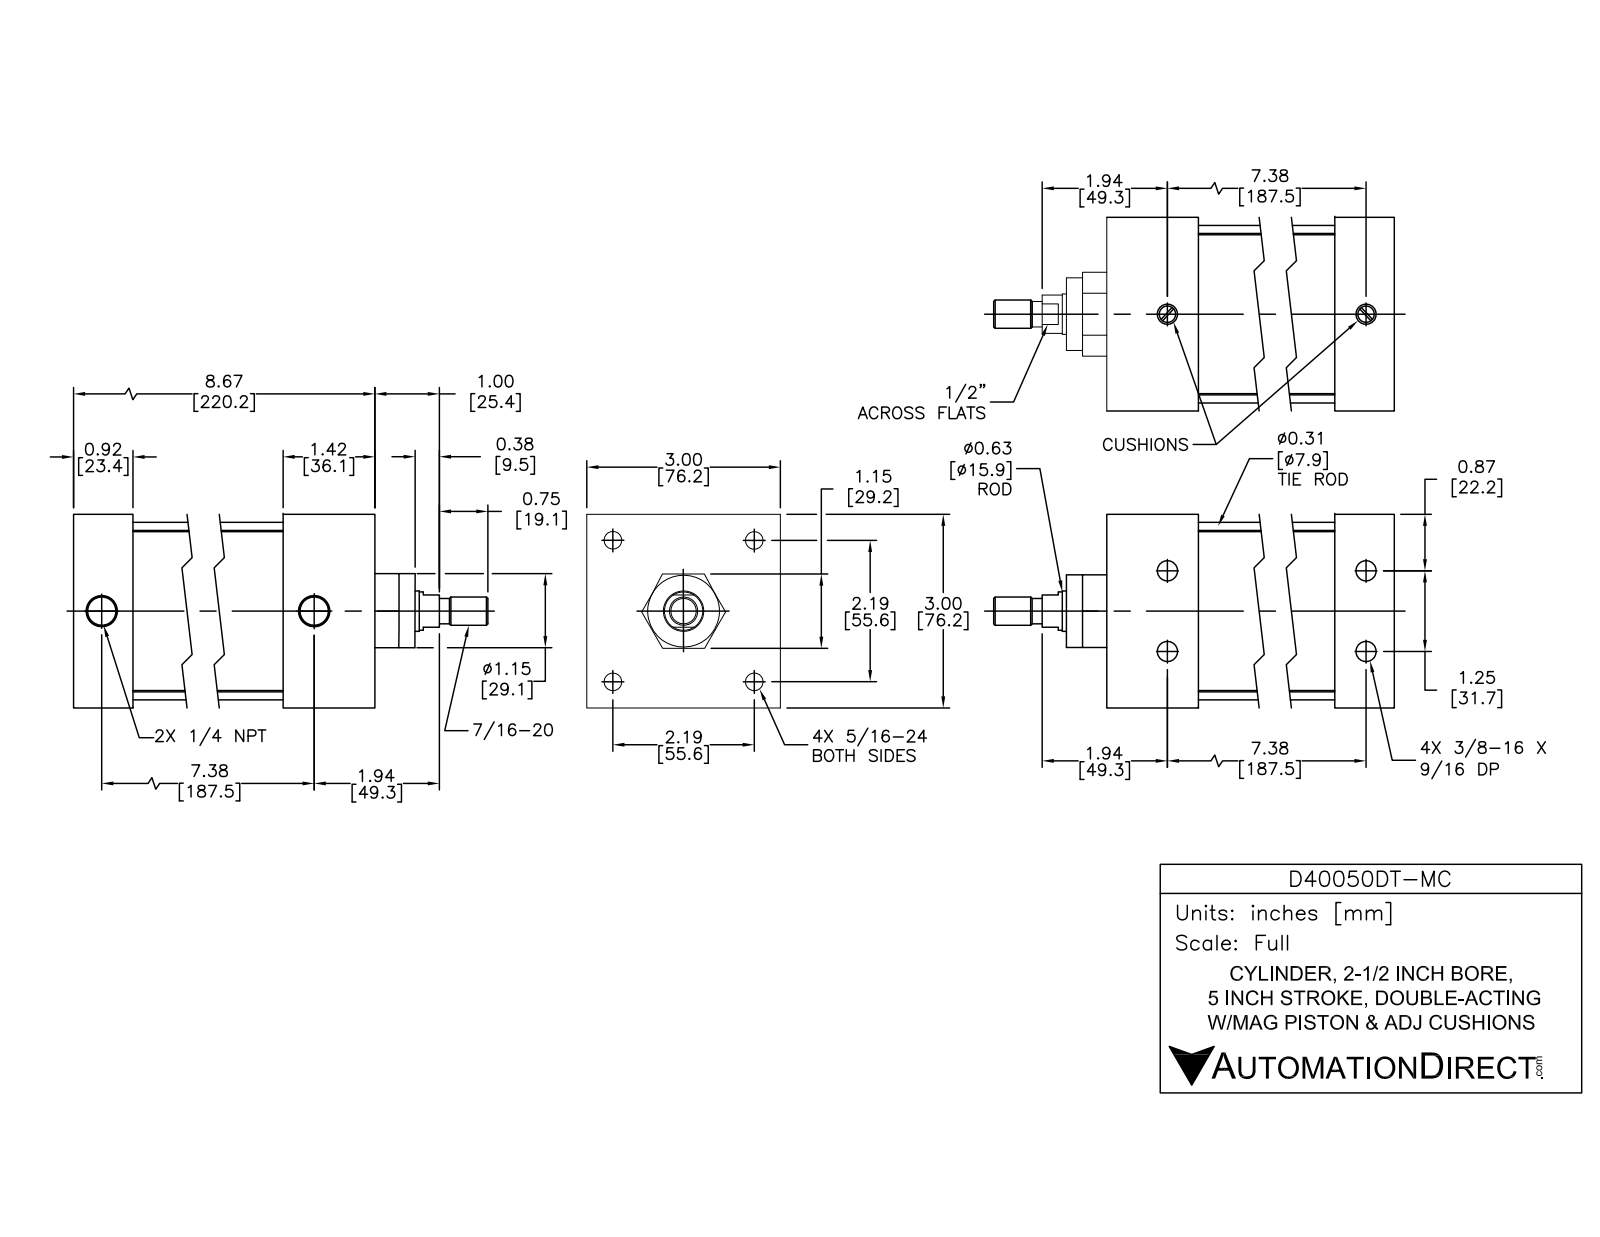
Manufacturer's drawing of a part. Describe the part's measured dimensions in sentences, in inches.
The part is named "D40050DT-MC; D40050DT-M PISTON; D40050DT-M BODY". Its 3-D file was written by "SolidWorks 2015 (AUTOMOTIVE_DESIGN)". It is 12 solids with 298 faces: 94 planar, 114 cylindrical and 90 other. Overall it measures 10.496 by 3 by 3 inches. Its volume is 37.14 cubic inches and its surface area 262.6 square inches. Round holes: 4 of diameter 0.267, 4 of diameter 0.307, 4 of diameter 0.359, 4 of diameter 0.5, 2 of diameter 0.297, 2 of diameter 0.477, 1 of diameter 0.625, 1 of diameter 0.628, 1 of diameter 2.5. Round bosses or shafts: 4 of diameter 0.484, 4 of diameter 0.313, 4 of diameter 0.282, 1 of diameter 2.75, 1 of diameter 2.497, 1 of diameter 1.12, 1 of diameter 0.622, 1 of diameter 0.59. Partial cylindrical surfaces (rounded edges, fillets, slot ends): 4 of radius 0.3. The main face-to-face distances are 3, 0.08, 6.326, 8.746, 7.726, 1.02, 1.42, 6.306, 7.326, 1. The hole center spacings are 1.556, 2.2, 7.396, 7.37, 0.625, 0.625, 1.25, 3.111.
